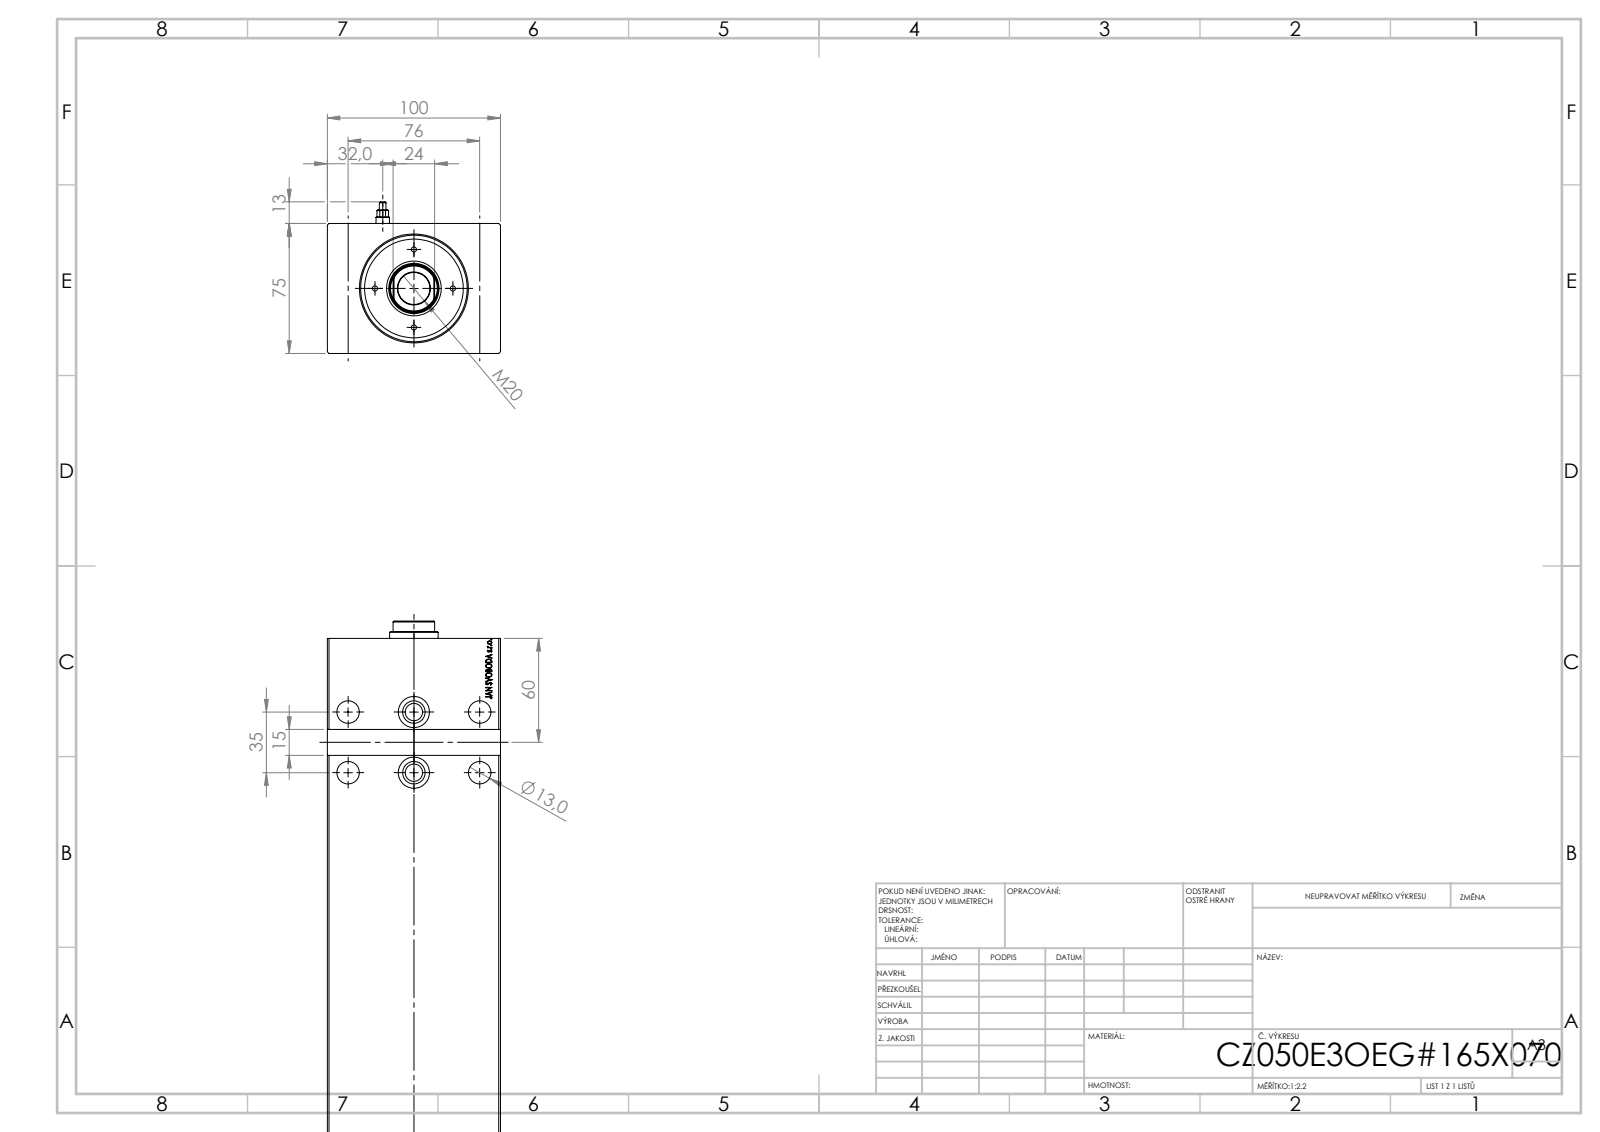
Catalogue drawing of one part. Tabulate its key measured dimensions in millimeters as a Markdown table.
| quantity | value |
| --- | --- |
| STEP written by | SolidWorks 2019 (CONFIG_CONTROL_DESIGN) |
| units | millimeters |
| bodies | 1 solid, 807 faces (395 planar, 30 cylindrical, 382 other) |
| overall size | 287 × 100 × 75 |
| volume | 1 569 000 mm³ |
| surface area | 169 659 mm² |
| round holes (diameter × count) | 13 × 4, 8 × 2, 10 × 2, 18 × 2, 36 × 1, 50 × 1, 61.5 × 1 |
| round bosses / shafts (diameter × count) | 13 × 2 |
| main face-to-face distances | 75, 100, 287, 269.2, 17.8, 2, 73, 286.8, 17.6, 10 |
| hole center spacings | 38, 51.66, 35, 76, 83.67, 18.82, 20.74, 44.32 |
